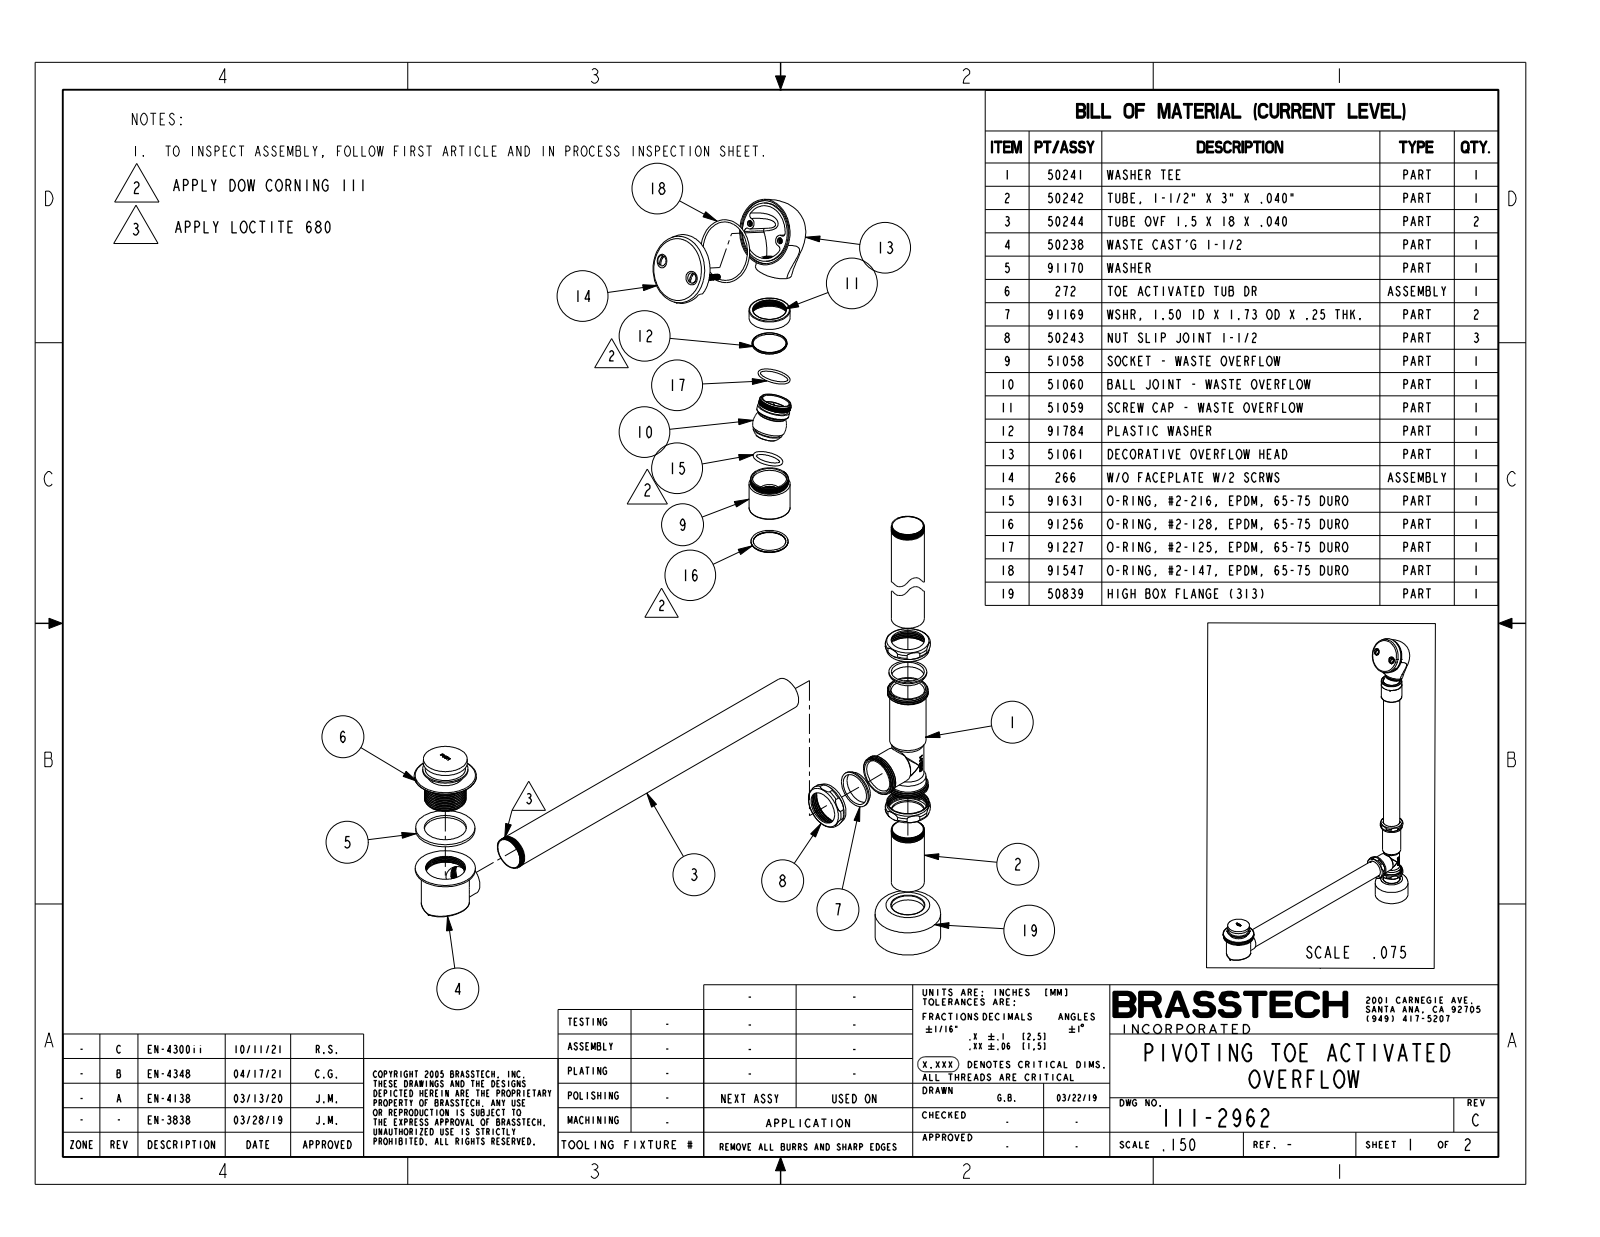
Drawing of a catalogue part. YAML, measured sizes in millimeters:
part_name: "50241; 50242; 50244; 50238 (+8 more)"
step_written_by: "CREO PARAMETRIC BY PTC INC, 2018400 (AUTOMOTIVE_DESIGN)"
units: millimeters
bodies: {solids: 28, faces: 1448, planar: 231, cylindrical: 627, other: 590}
overall_size: [724.6, 585.7, 80.8]
volume: 441500
surface_area: 485700
round_holes:
  - {diameter: 38.6, count: 4}
  - {diameter: 45.3, count: 3}
  - {diameter: 4.9, count: 2}
  - {diameter: 6.9, count: 2}
  - {diameter: 36.1, count: 2}
  - {diameter: 6.4, count: 1}
  - {diameter: 23.1, count: 1}
  - {diameter: 24.1, count: 1}
  - {diameter: 25.3, count: 1}
  - {diameter: 25.4, count: 1}
  - {diameter: 29.2, count: 1}
  - {diameter: 29.3, count: 1}
round_bosses_or_shafts:
  - {diameter: 38.1, count: 3}
  - {diameter: 49.3, count: 2}
  - {diameter: 47.5, count: 2}
  - {diameter: 43.9, count: 2}
  - {diameter: 42.2, count: 2}
  - {diameter: 12.2, count: 2}
  - {diameter: 6.2, count: 2}
  - {diameter: 76.2, count: 1}
partial_cylinders:
  - {radius: 1, count: 5}
  - {radius: 6.4, count: 2}
  - {radius: 26.2, count: 2}
  - {radius: 1.4, count: 1}
  - {radius: 7, count: 1}
  - {radius: 14.9, count: 1}
  - {radius: 18.3, count: 1}
  - {radius: 20.1, count: 1}
face_to_face_distances: [6.7, 3.7, 3, 2, 446, 21.2, 50, 12.4, 5.1, 8.8]
hole_center_spacings: [24.6, 49.3, 503.1]
